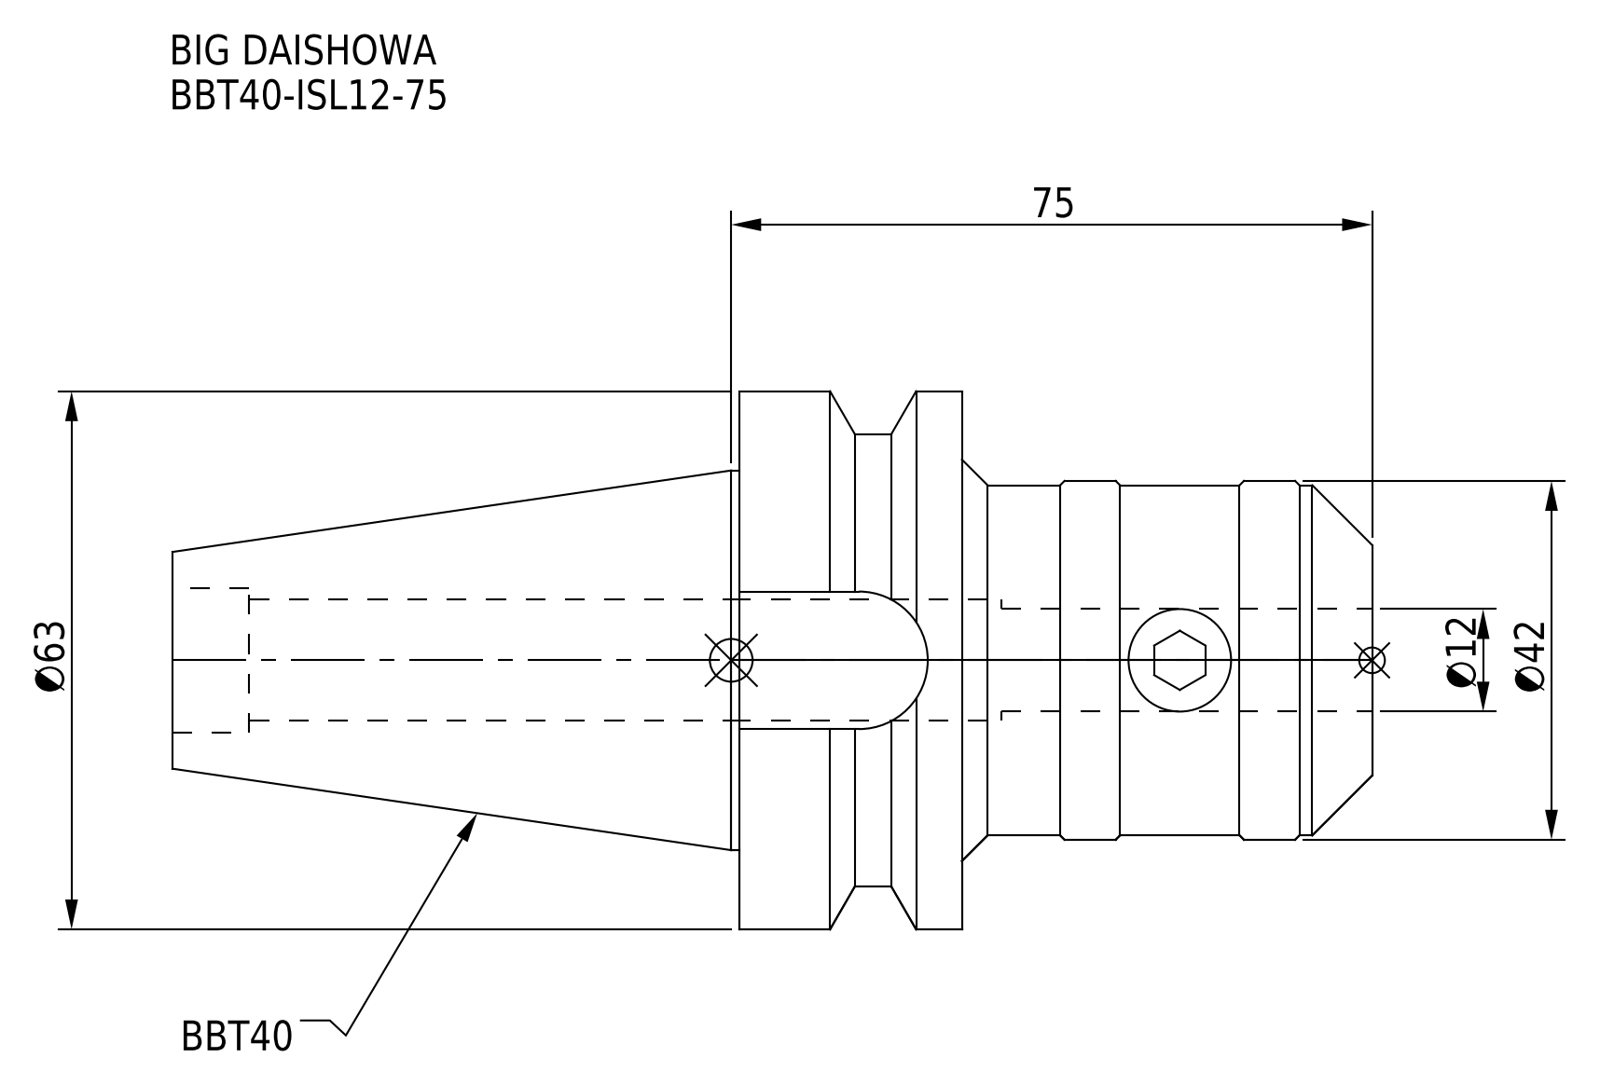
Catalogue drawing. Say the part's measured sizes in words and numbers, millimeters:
The part is named "BBT40-ISL12-75". Its 3-D file was written by "CREO PARAMETRIC BY PTC INC, 2016380 (AUTOMOTIVE_DESIGN)". It is 1 solid with 58 faces: 12 planar, 28 cylindrical and 18 other. Overall it measures 140.4 by 63 by 63 millimeters. Its volume is 176 723 cubic millimeters and its surface area 30 153 square millimeters. Round holes: 1 of diameter 12, 1 of diameter 14.2, 1 of diameter 17. Round bosses or shafts: 1 of diameter 63, 1 of diameter 53, 1 of diameter 44.45, 1 of diameter 42, 1 of diameter 41. Partial cylindrical surfaces (rounded edges, fillets, slot ends): 1 of radius 8.05. The main face-to-face distances are 26, 48, 74, 45, 140.4, 92.4, 66.4, 16.1, 131.4, 83.4.
